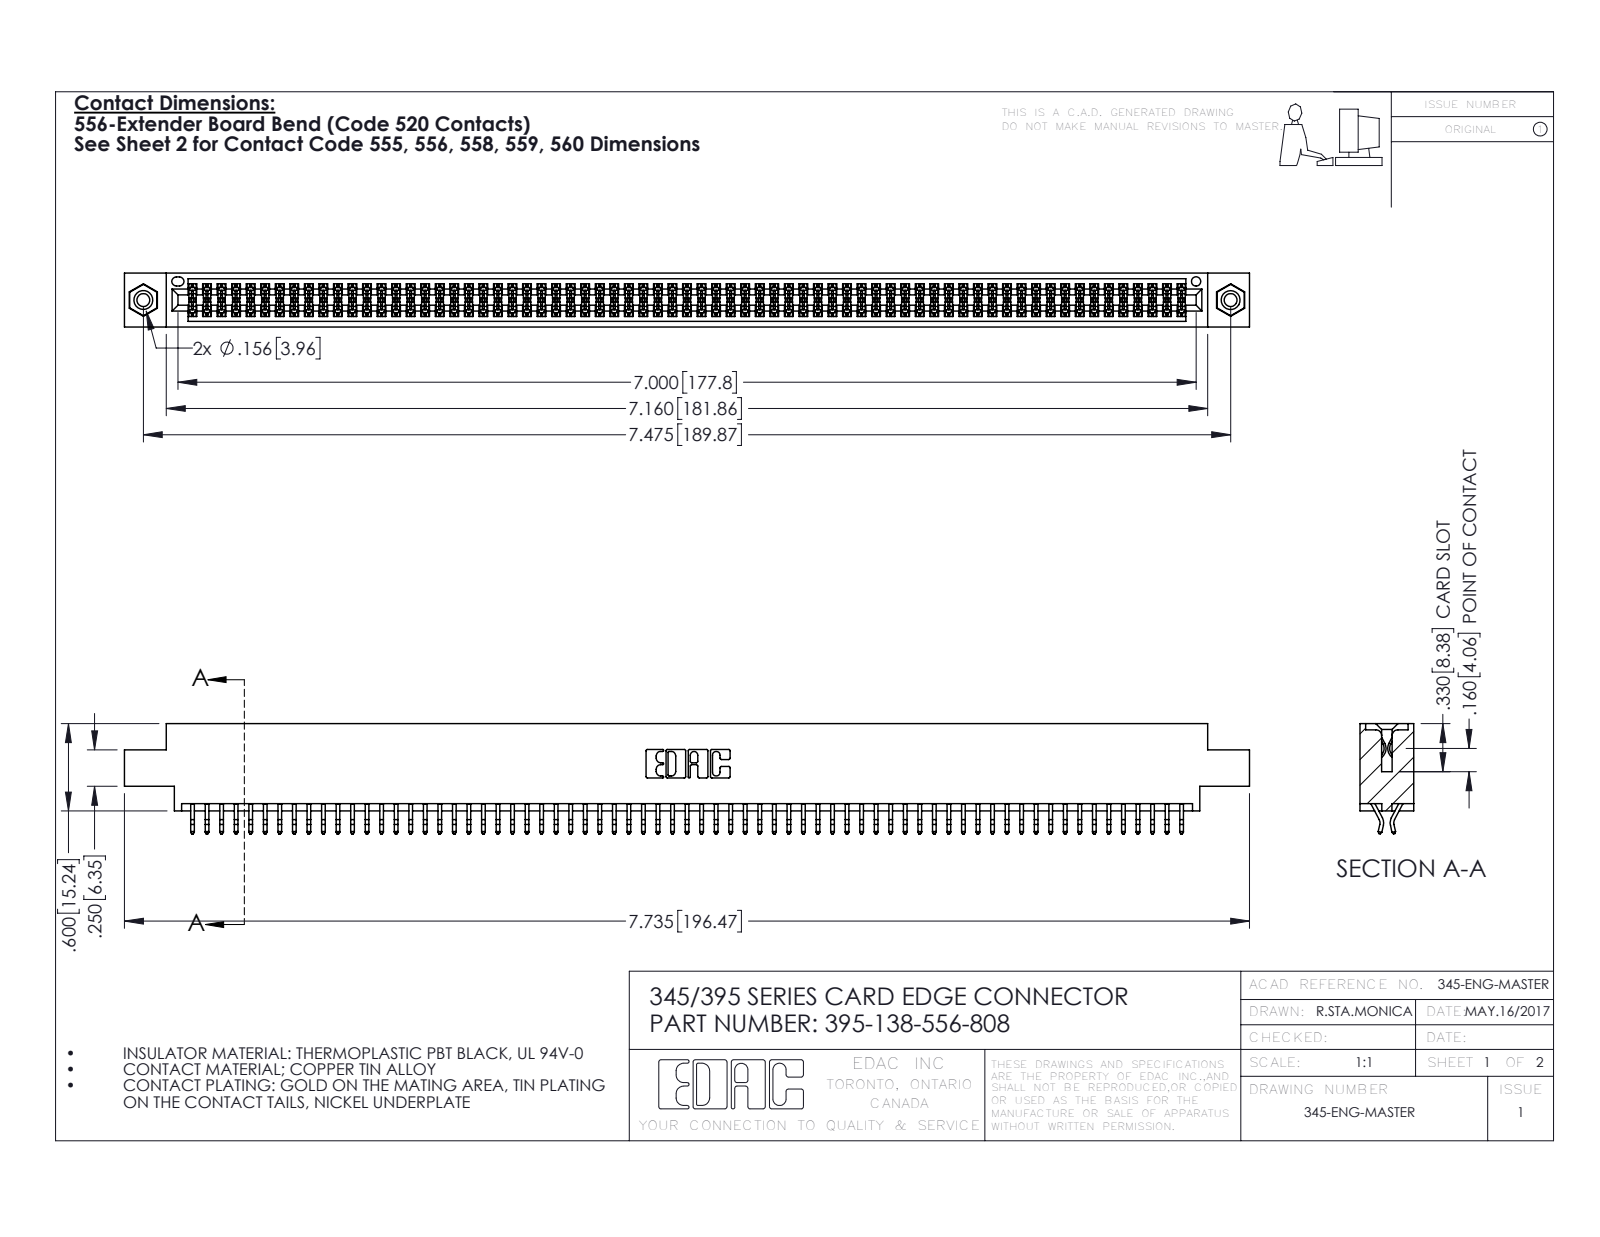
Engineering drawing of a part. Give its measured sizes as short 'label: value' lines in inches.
name: 345-292-001_556 Tail; 345-250-001_345-250-003-102; 345 Part_0.170 Offset - 0.156 Dia-TI; 395-138-556-808
written by: SolidWorks 2016 (CONFIG_CONTROL_DESIGN)
unit: in
bodies: 141 solids, 7918 faces (5222 planar, 2680 cylindrical, 16 other)
size: 7.735 × 0.757 × 0.37
volume: 1.172 in³; area: 44.88 in²
holes: 2× ⌀0.089, 2× ⌀0.125, 2× ⌀0.156, 1× ⌀0.064
bosses: 2× ⌀0.155
rounds: 207× R0.006, 22× R0.01, 6× R0.007, 6× R0.031, 3× R0.026, 2× R0.01, 2× R0.014, 2× R0.019
face distances: 0.072, 0.298, 0.37, 0.2, 0.025, 0.098, 0.272, 0.225, 0.175, 0.149
hole spacings: 0.27, 7.239, 7.475
